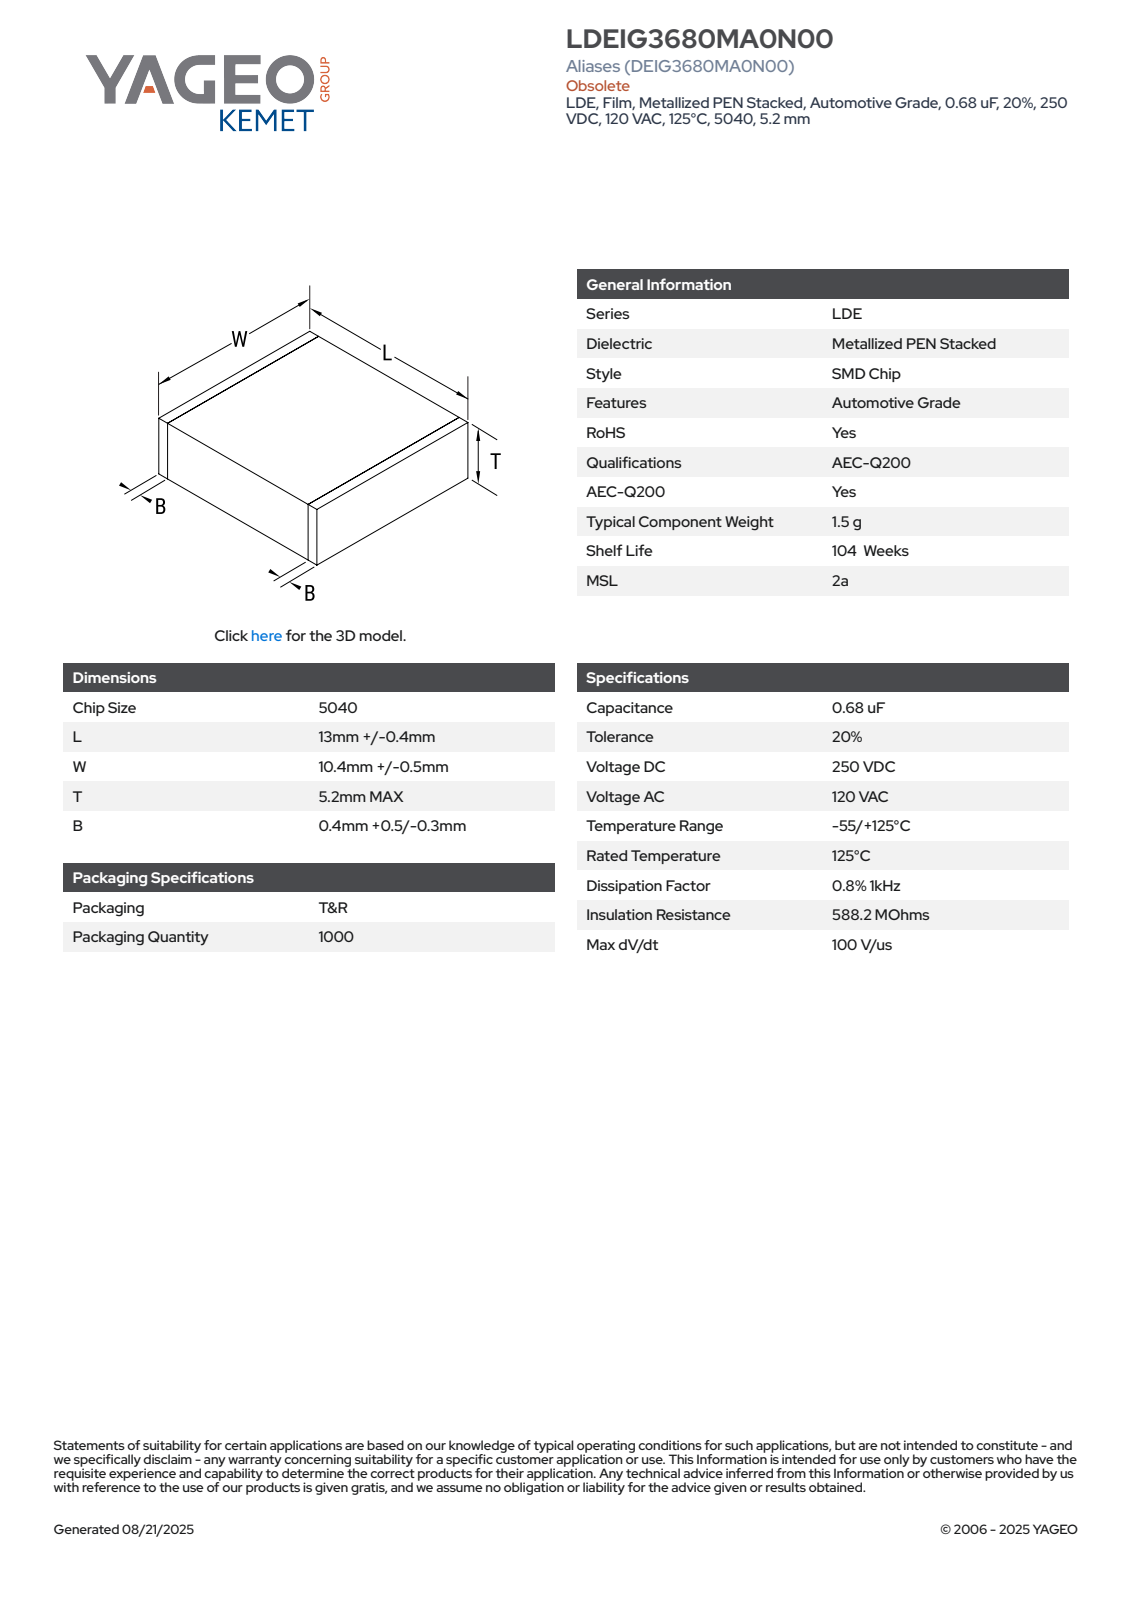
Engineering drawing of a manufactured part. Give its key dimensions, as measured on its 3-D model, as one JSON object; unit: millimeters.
{"part_name": "CFS_LDELDB_5040_L13.4W10.9T5.2B0.9", "step_written_by": "SolidWorks 2020 (AUTOMOTIVE_DESIGN)", "units": "millimeters", "bodies": {"solids": 4, "faces": 73, "planar": 73, "cylindrical": 0, "other": 0}, "overall_size": [13.4, 10.9, 5.2], "volume_mm3": 756, "surface_area_mm2": 553, "face_to_face_distances": [5.18, 10.88, 13.4, 5.19, 5.2, 10.89, 10.9, 0.5, 12.9, 12.4]}
